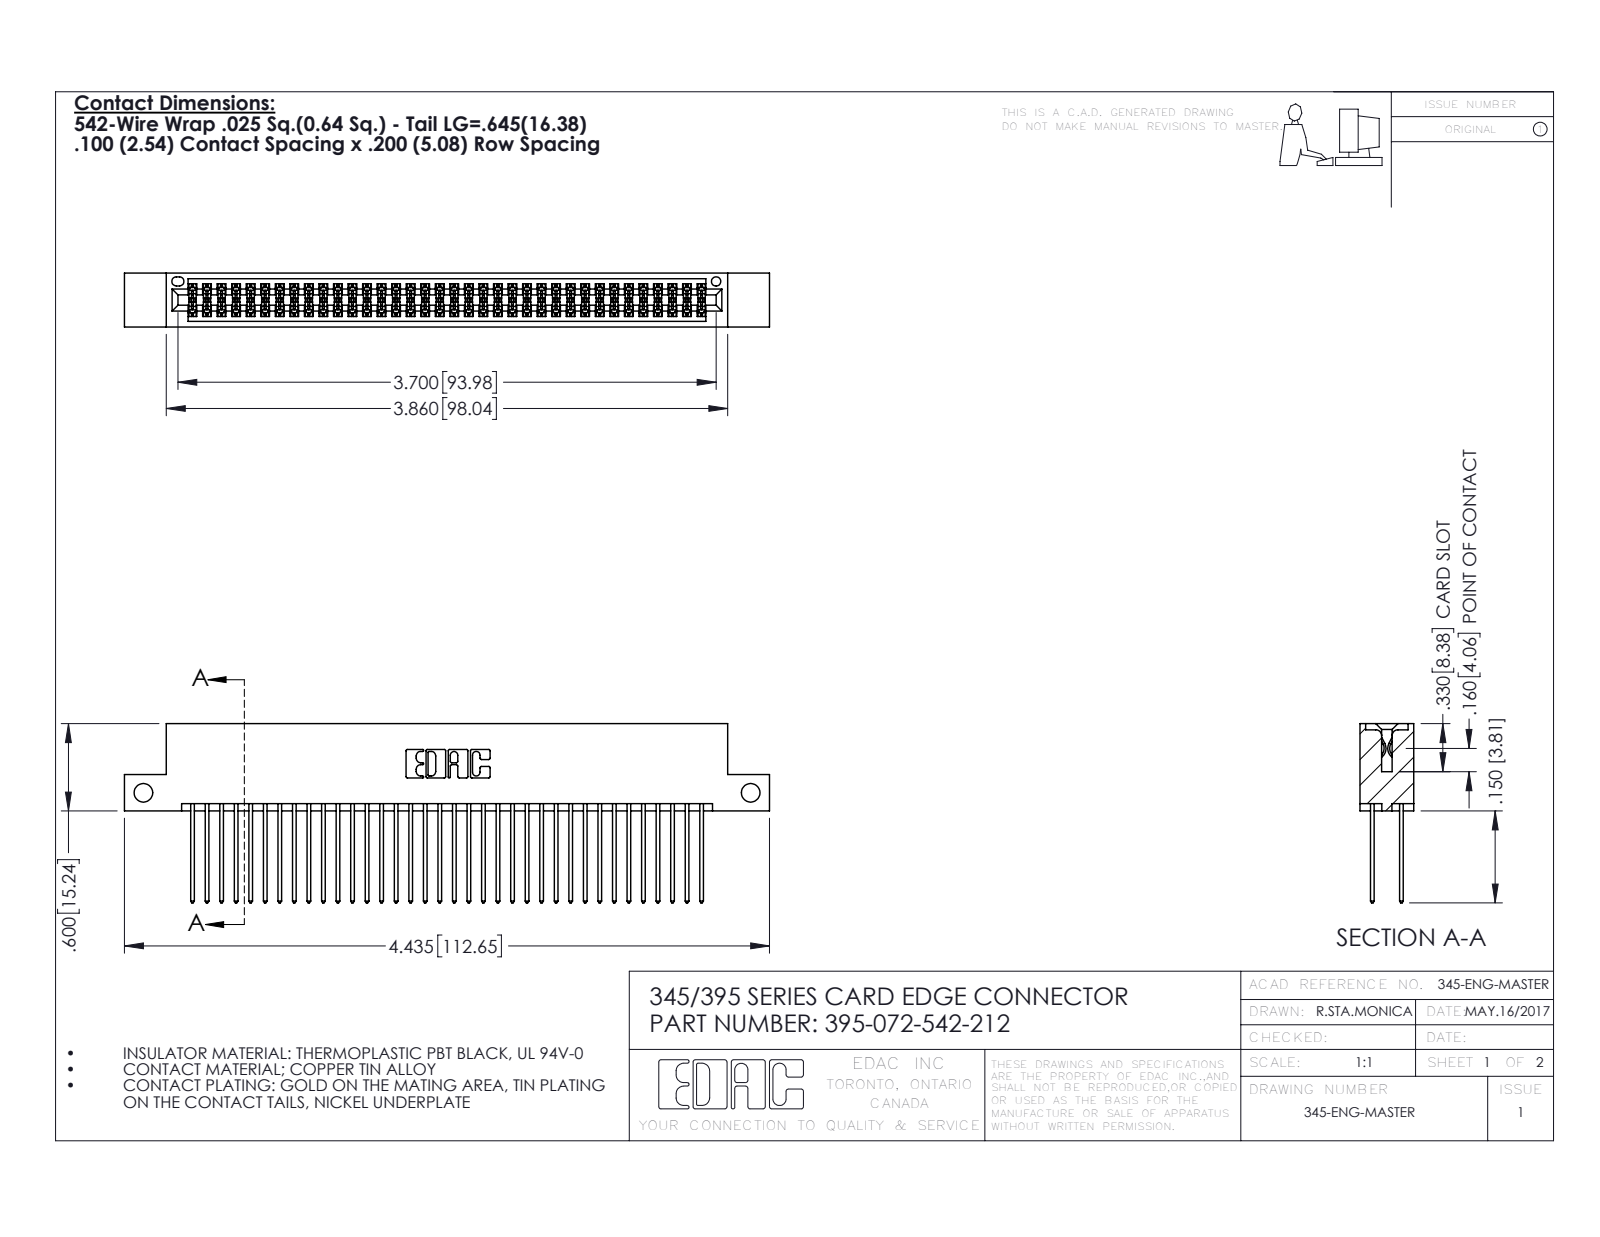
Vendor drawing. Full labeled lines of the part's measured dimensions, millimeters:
Part name (STEP PRODUCT): 345-292-001_345-293-142; 395-072-542-212; 345 Part_Flush Mounting Lugs - Side Mount
STEP written by: SolidWorks 2016 (CONFIG_CONTROL_DESIGN)
Units: millimetres
Bodies: 73 solids, 3726 faces (2456 planar, 1270 cylindrical, 0 other)
Overall size (bounding box): 112.6 × 31.3 × 9.4
Volume: 11 100 mm³ · Surface area: 17 770 mm²
Round holes (diameter × count): ⌀3.3 ×2, ⌀1.6 ×1
Partial cylindrical surfaces — rounded edges, fillets, slot ends (radius × count): R0.2 ×108, R0.3 ×72, R0.3 ×22, R0.2 ×6, R0.8 ×6, R0.7 ×3, R0.4 ×2, R0.5 ×2
Main face-to-face distances: 7.6, 1.8, 5.1, 2.5, 6.9, 0.6, 9.4, 5.7, 4.4, 3.8
Hole centre spacings: 106
